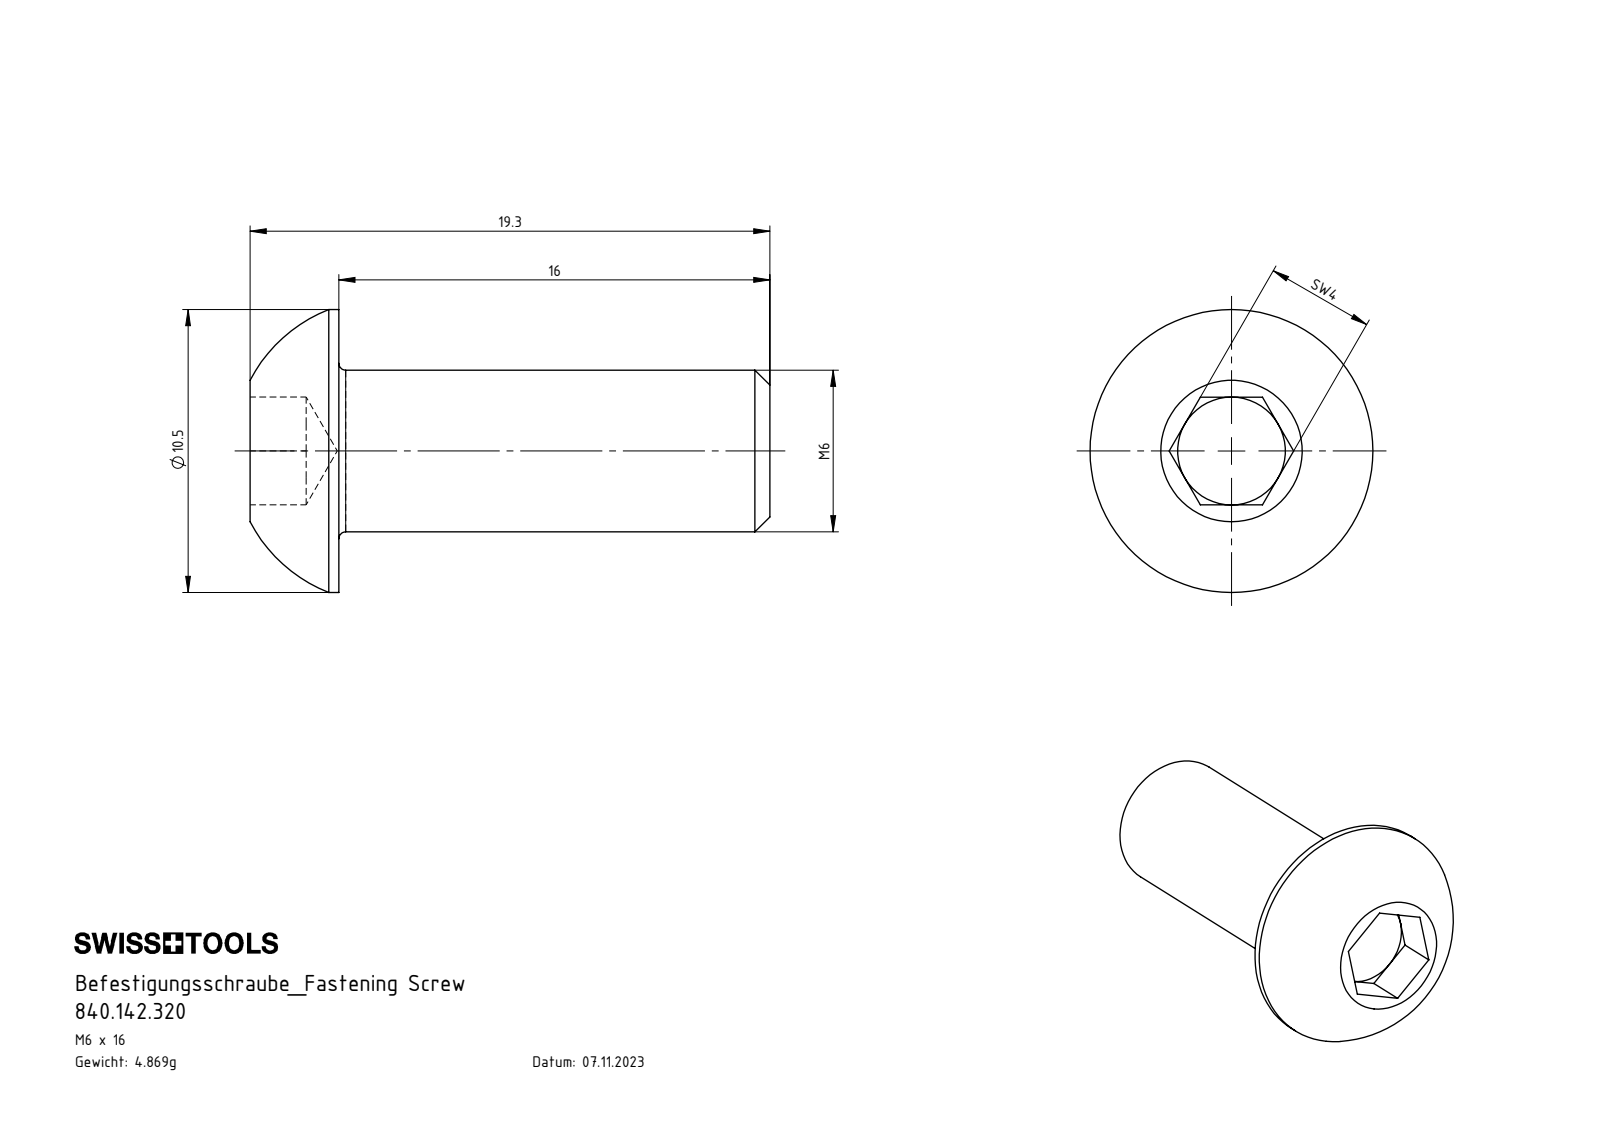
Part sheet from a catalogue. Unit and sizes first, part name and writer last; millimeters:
Units: millimetres
Overall size (bounding box): 19.3 × 10.5 × 10.5
Round bosses / shafts (diameter × count): ⌀10.5 ×1, ⌀6 ×1
Main face-to-face distances: 16, 4, 3.3, 19.3, 2.08, 1.22, 17.22
Volume: 620 mm³ · Surface area: 548 mm²
Bodies: 1 solid, 27 faces (15 planar, 4 cylindrical, 8 other)
Part name (STEP PRODUCT): 840.142.320
STEP written by: SolidWorks 2022 (AUTOMOTIVE_DESIGN)
